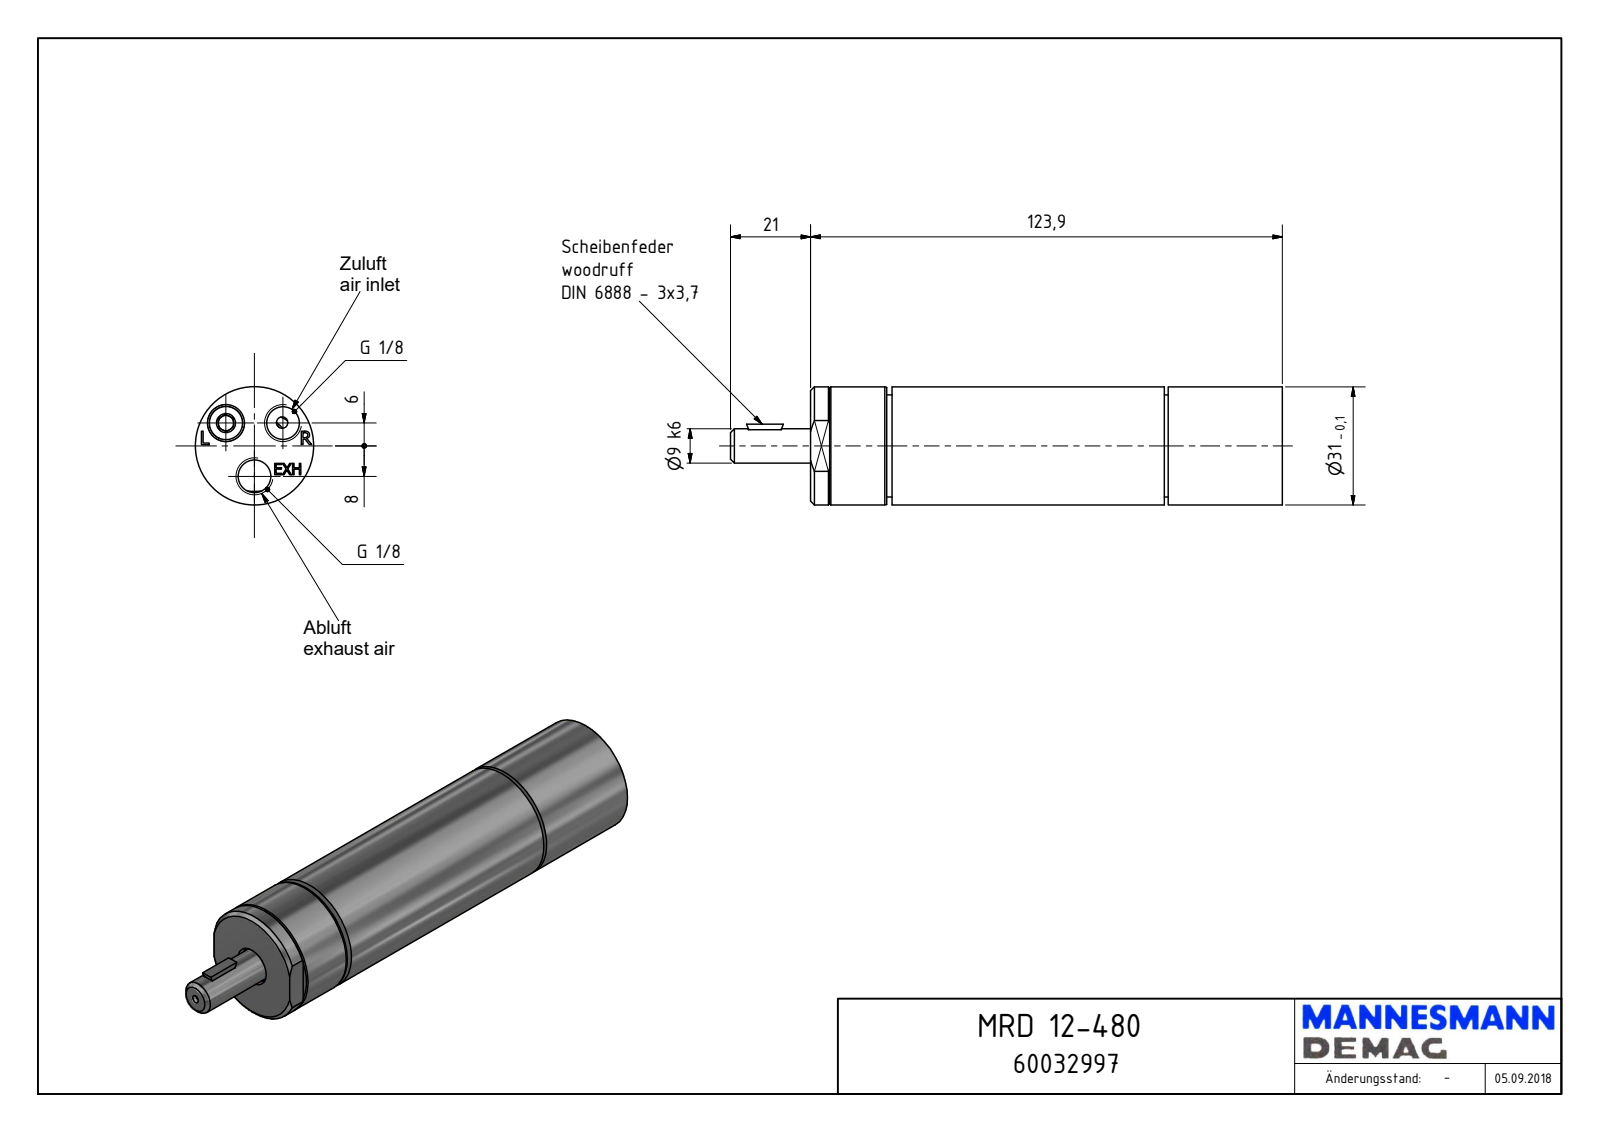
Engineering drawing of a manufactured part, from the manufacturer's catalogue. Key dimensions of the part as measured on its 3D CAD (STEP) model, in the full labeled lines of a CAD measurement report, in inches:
Part name (STEP PRODUCT): MRD 12-480_60032997
STEP written by: Autodesk Inventor 2018 (AUTOMOTIVE_DESIGN)
Units: inches
Bodies: 1 solid, 153 faces (101 planar, 27 cylindrical, 25 other)
Overall size (bounding box): 5.705 × 1.22 × 1.22
Volume: 5.632 in³ · Surface area: 25.99 in²
Round holes (diameter × count): ⌀0.337 ×3, ⌀0.039 ×1, ⌀0.157 ×1, ⌀0.413 ×1, ⌀1.154 ×1
Round bosses / shafts (diameter × count): ⌀1.22 ×1, ⌀1.102 ×1, ⌀1.055 ×1, ⌀0.354 ×1
Partial cylindrical surfaces — rounded edges, fillets, slot ends (radius × count): R0.157 ×2, R0.197 ×1, R0.207 ×1, R0.45 ×1, R0.472 ×1
Main face-to-face distances: 4.878, 3.657, 0.843, 4.035, 2.815, 1.22, 0.039, 3.697, 2.854, 1.181
Hole centre spacings: 0.378, 0.625, 0.315, 0.591
